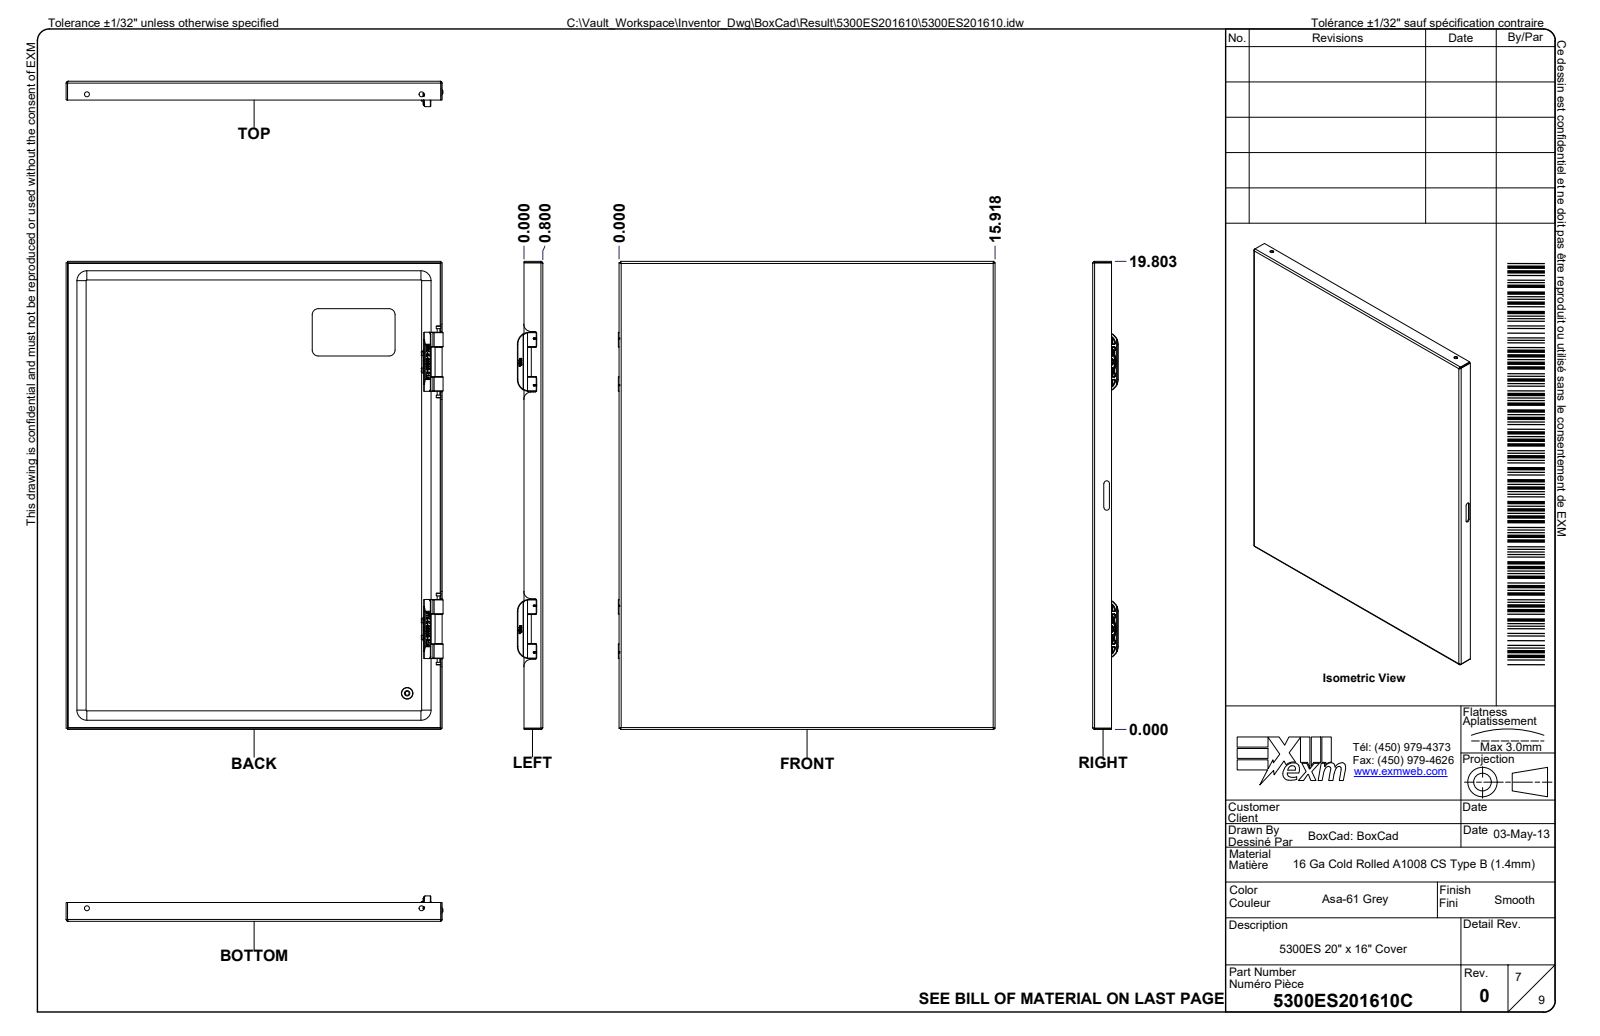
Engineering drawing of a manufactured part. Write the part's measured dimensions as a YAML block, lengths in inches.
part_name: "5300ES201610; 5300ES201610B; 5300ES201610B-P; STK-Q-16005 (+8 more)"
step_written_by: "Autodesk Inventor 2024 (AUTOMOTIVE_DESIGN)"
units: inches
bodies: {solids: 45, faces: 5491, planar: 1475, cylindrical: 1539, other: 2477}
overall_size: [20, 16.923, 11.104]
volume: 114.5
surface_area: 3720
round_holes:
  - {diameter: 0.043, count: 8}
  - {diameter: 0.03, count: 6}
  - {diameter: 0.315, count: 5}
  - {diameter: 0.178, count: 4}
  - {diameter: 0.27, count: 4}
  - {diameter: 0.29, count: 4}
  - {diameter: 0.39, count: 4}
  - {diameter: 0.201, count: 3}
  - {diameter: 0.187, count: 2}
  - {diameter: 0.203, count: 2}
  - {diameter: 0.22, count: 2}
  - {diameter: 0.33, count: 2}
round_bosses_or_shafts:
  - {diameter: 0.039, count: 8}
  - {diameter: 0.03, count: 6}
  - {diameter: 0.232, count: 5}
  - {diameter: 0.717, count: 4}
  - {diameter: 0.311, count: 4}
  - {diameter: 0.262, count: 4}
  - {diameter: 0.472, count: 2}
  - {diameter: 0.287, count: 2}
partial_cylinders:
  - {radius: 0.039, count: 85}
  - {radius: 0.02, count: 79}
  - {radius: 0.01, count: 66}
  - {radius: 0.008, count: 60}
  - {radius: 0.031, count: 36}
  - {radius: 0.016, count: 30}
  - {radius: 0.084, count: 28}
  - {radius: 0.004, count: 16}
face_to_face_distances: [0.053, 15.947, 0.053, 10.998, 11.052, 19.947, 11.104, 11.051, 0.927, 0.874]
hole_center_spacings: [11.303, 1, 1.591, 12.25, 13.422, 15.25, 17.411, 21.927]
